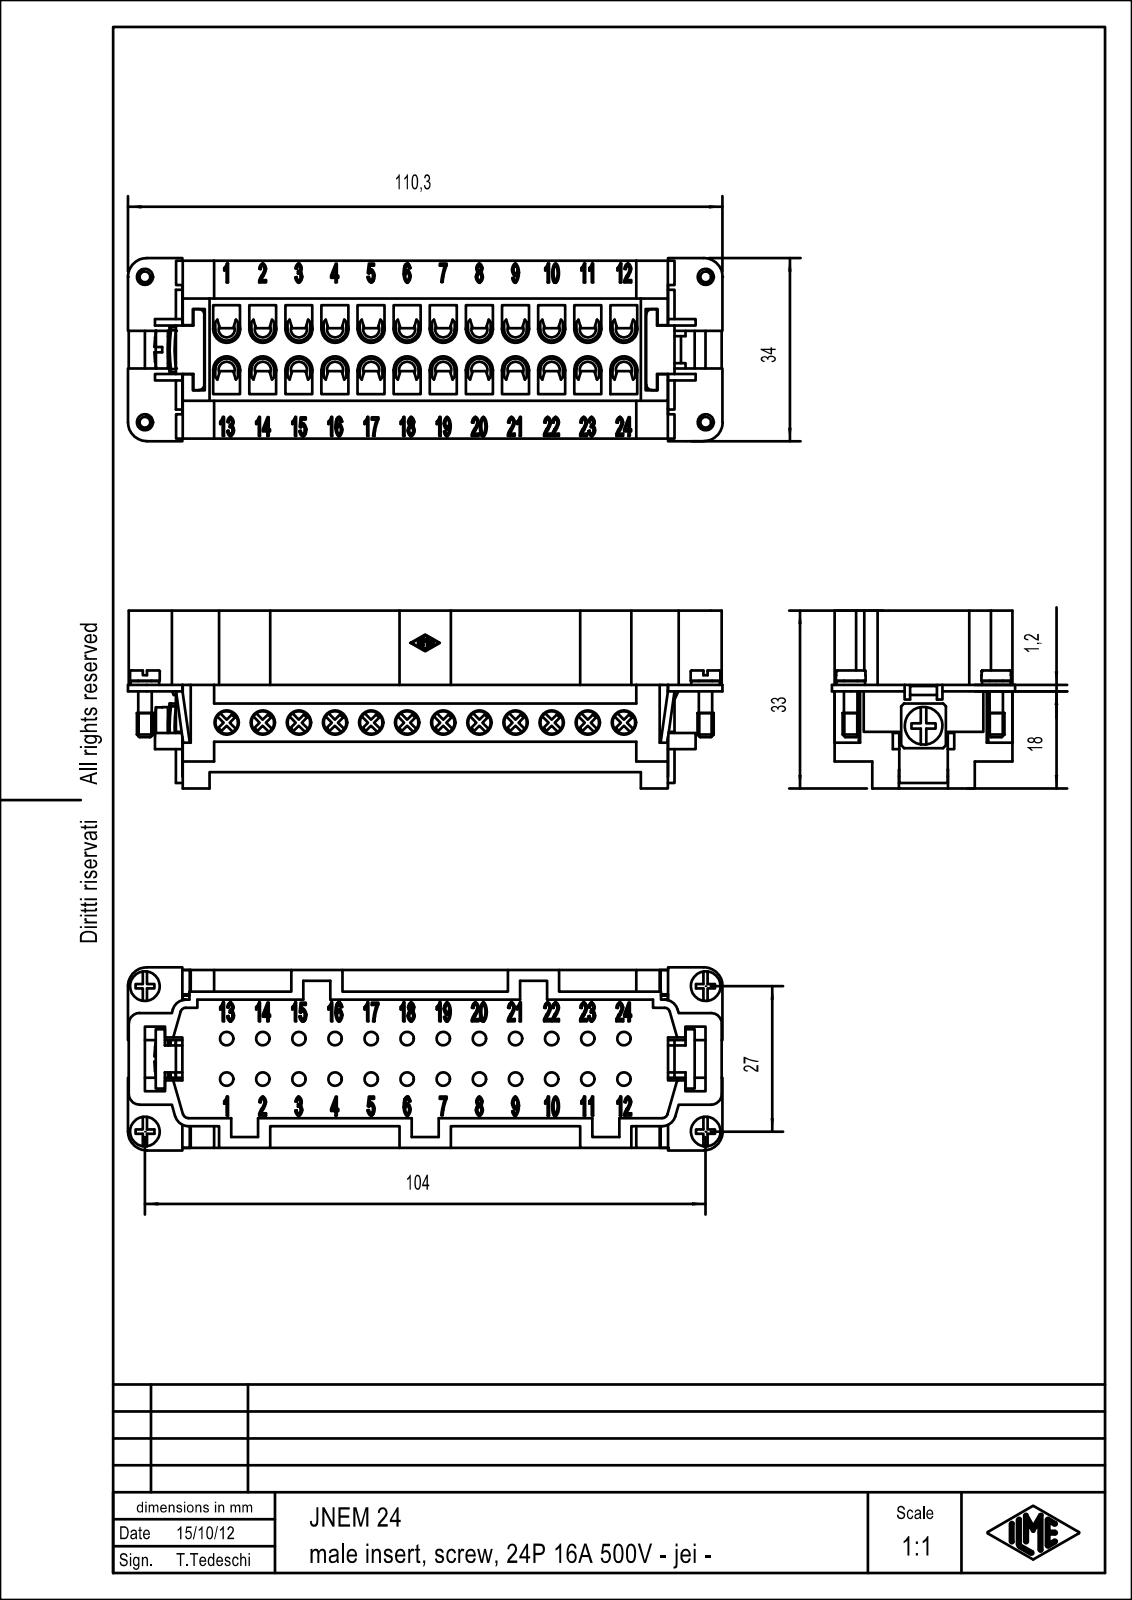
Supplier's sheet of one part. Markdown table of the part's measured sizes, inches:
| quantity | value |
| --- | --- |
| part name | JNEM_24 |
| STEP written by | Creo Elements/Direct Modeling 18.0B 02-Dec-2011 (C) Parametric Technology GmbH (AUTOMOTIVE_DESIGN) |
| units | inches |
| bodies | 1 solid, 2459 faces (1513 planar, 334 cylindrical, 612 other) |
| overall size | 4.343 × 1.339 × 1.299 |
| volume | 2.711 in³ |
| surface area | 58.8 in² |
| round holes (diameter × count) | 0.118 × 24, 0.177 × 12, 0.1 × 4, 0.128 × 1 |
| round bosses / shafts (diameter × count) | 0.098 × 28, 0.165 × 12, 0.217 × 4, 0.209 × 4, 0.118 × 4, 0.276 × 1 |
| partial cylindrical surfaces (radius × count) | 0.098 × 28, 0.083 × 24, 0.004 × 14, 0.039 × 8, 0.079 × 6, 0.138 × 4, 0.217 × 1 |
| main face-to-face distances | 0.059, 0.866, 0.217, 0.157, 0.118, 0.925, 0.276, 0.807, 1.142, 1.083 |
| hole center spacings | 0.264, 0.528, 0.791, 1.055, 0.396, 1.319, 0.605, 0.844 |
